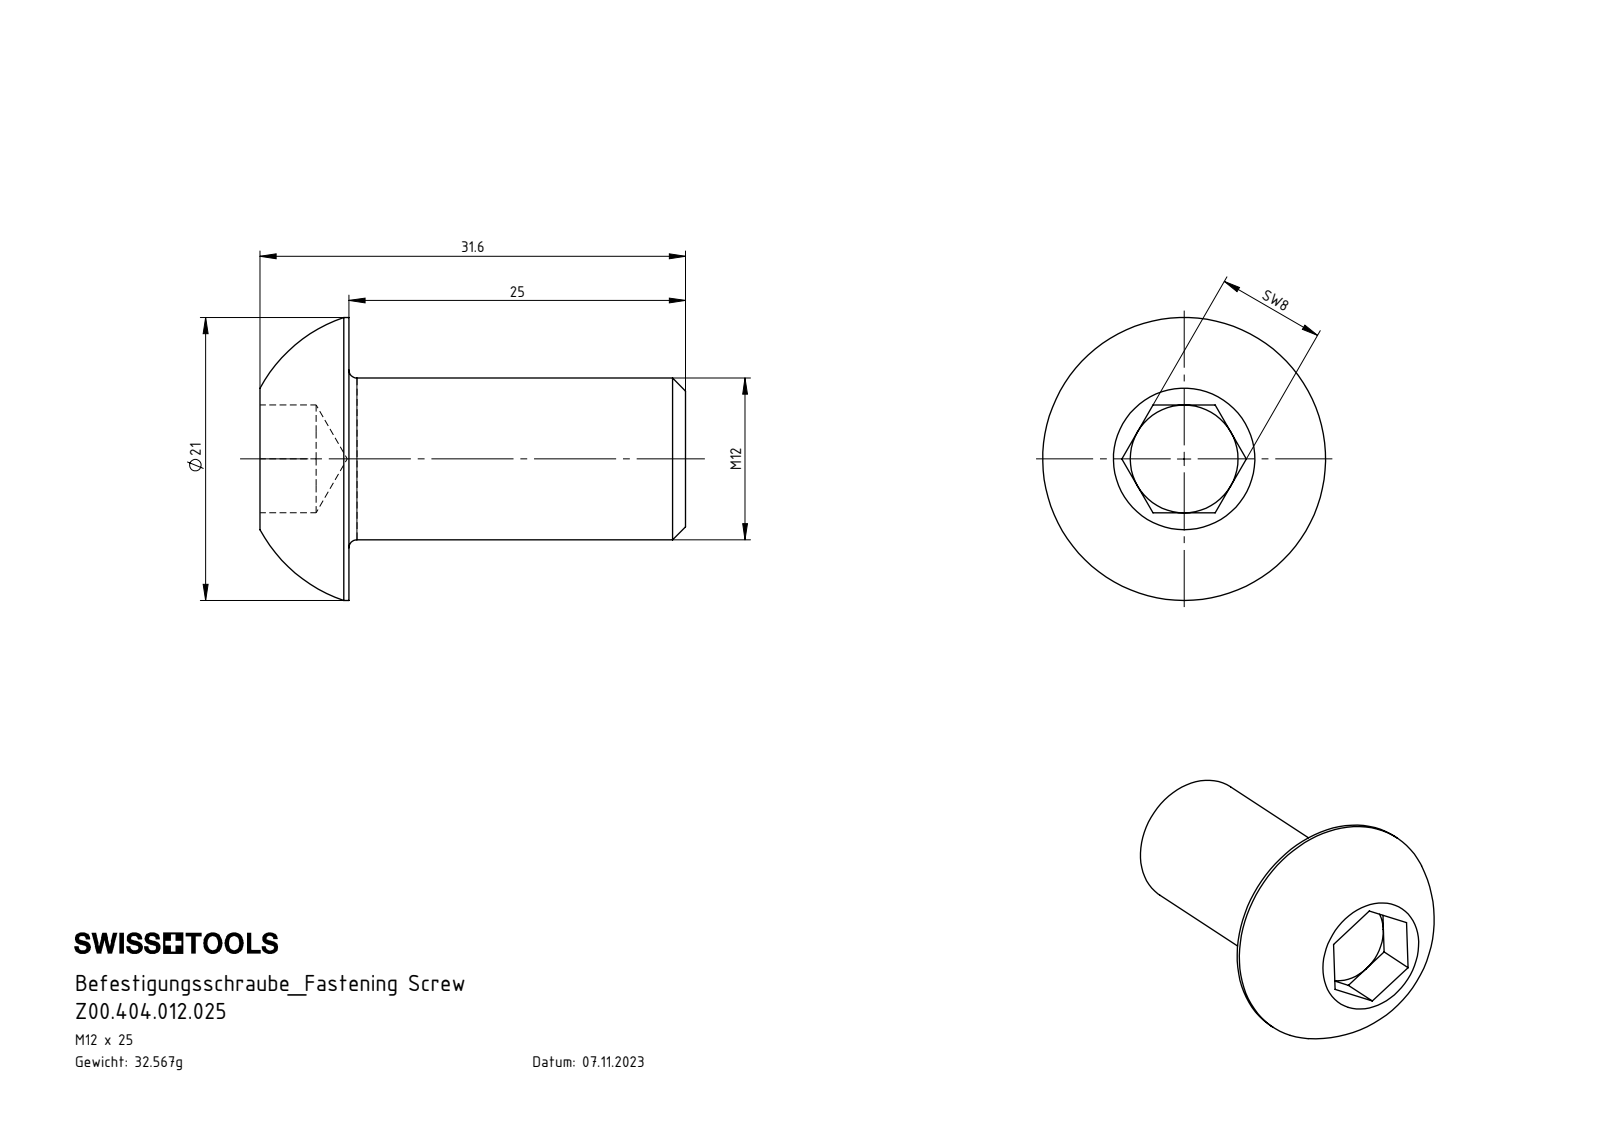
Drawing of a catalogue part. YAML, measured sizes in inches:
part_name: "Z00.404.012.025"
step_written_by: "SolidWorks 2022 (AUTOMOTIVE_DESIGN)"
units: inches
bodies: {solids: 1, faces: 27, planar: 15, cylindrical: 4, other: 8}
overall_size: [1.244, 0.827, 0.827]
volume: 0.253
surface_area: 2.984
round_bosses_or_shafts:
  - {diameter: 0.827, count: 1}
  - {diameter: 0.472, count: 1}
face_to_face_distances: [0.984, 0.315, 0.26, 1.244, 0.164, 0.096, 1.08]
